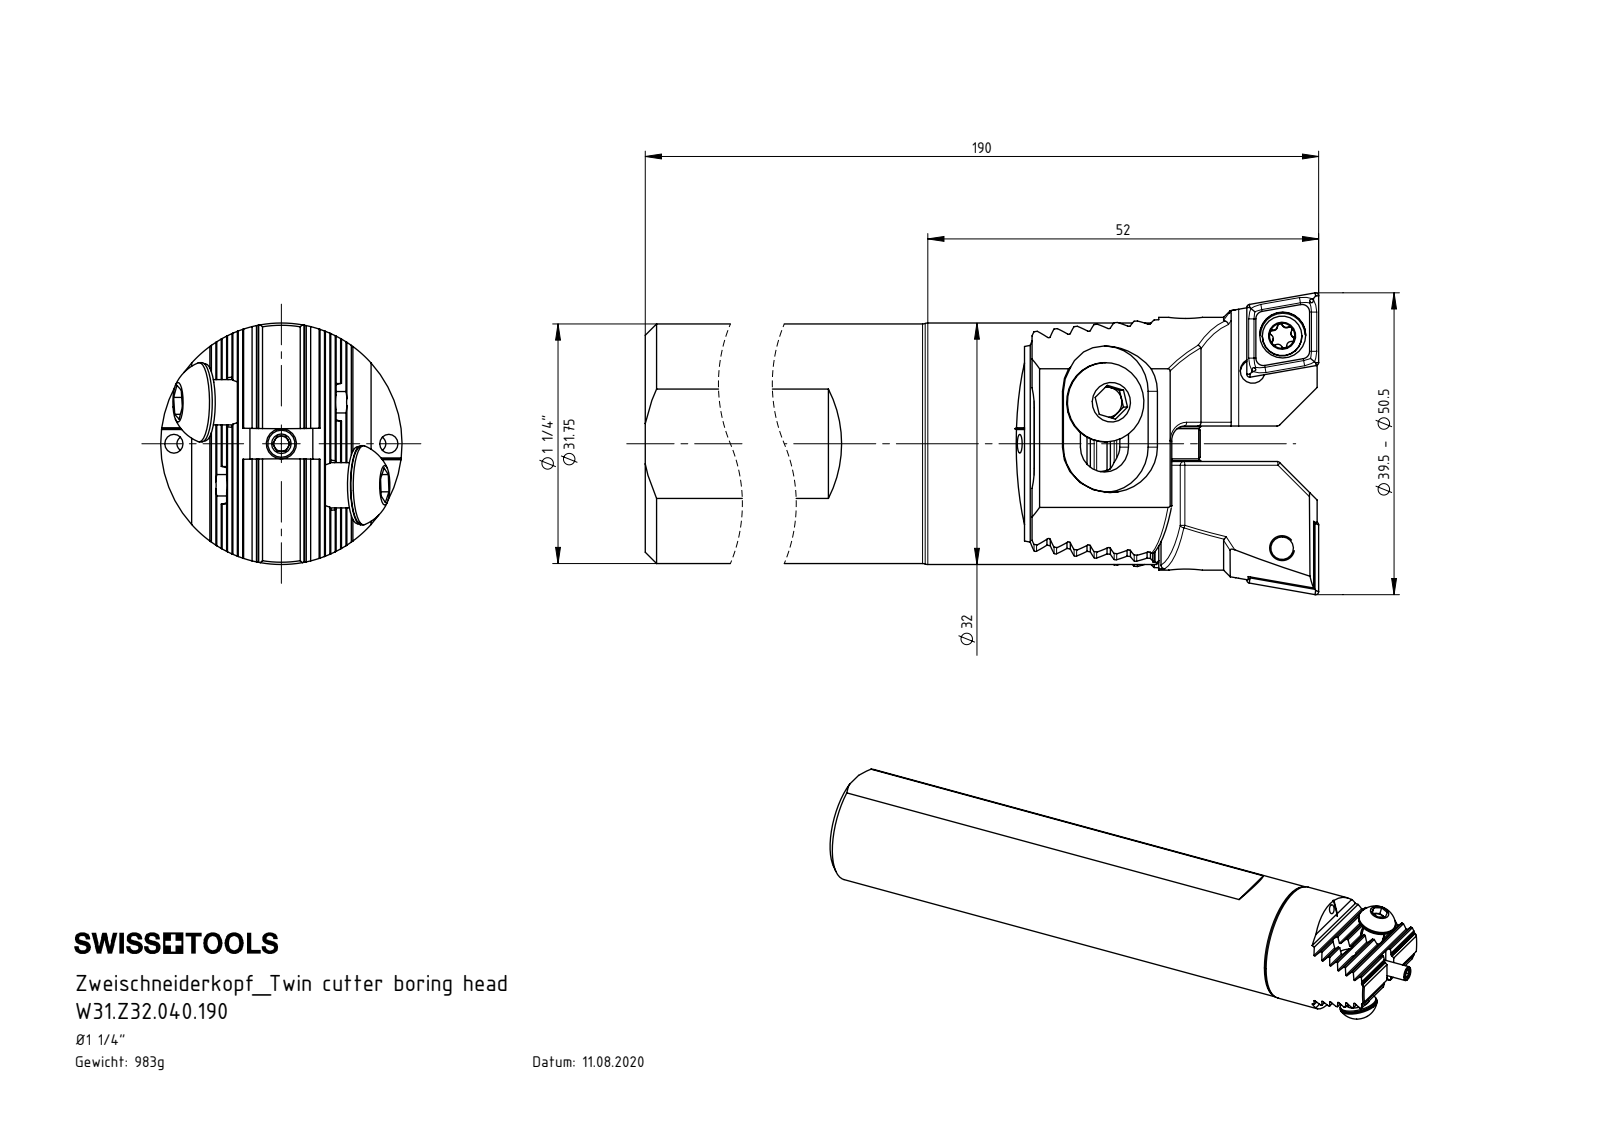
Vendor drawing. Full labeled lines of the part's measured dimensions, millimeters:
Part name (STEP PRODUCT): Z32-ER1.002.016_A; Z20-ER2.001.013_A; Z32-ER1.001.016; W31-Z32.K23.190_B (+1 more)
STEP written by: SolidWorks 2022 (CONFIG_CONTROL_DESIGN)
Units: millimetres
Bodies: 4 solids, 276 faces (142 planar, 75 cylindrical, 59 other)
Overall size (bounding box): 174.3 × 32 × 32
Volume: 113 312 mm³ · Surface area: 24 847 mm²
Round holes (diameter × count): ⌀2.5 ×4, ⌀5 ×2, ⌀6.8 ×2, ⌀2 ×1, ⌀10 ×1
Round bosses / shafts (diameter × count): ⌀10.5 ×2, ⌀6 ×2, ⌀32 ×1, ⌀31.75 ×1, ⌀4 ×1, ⌀3 ×1, ⌀2.2 ×1
Partial cylindrical surfaces — rounded edges, fillets, slot ends (radius × count): R0.2 ×14, R220 ×2
Main face-to-face distances: 2.38, 4.76, 7.14, 9.53, 7.15, 4.77, 11.91, 2.39, 9.52, 168.8
